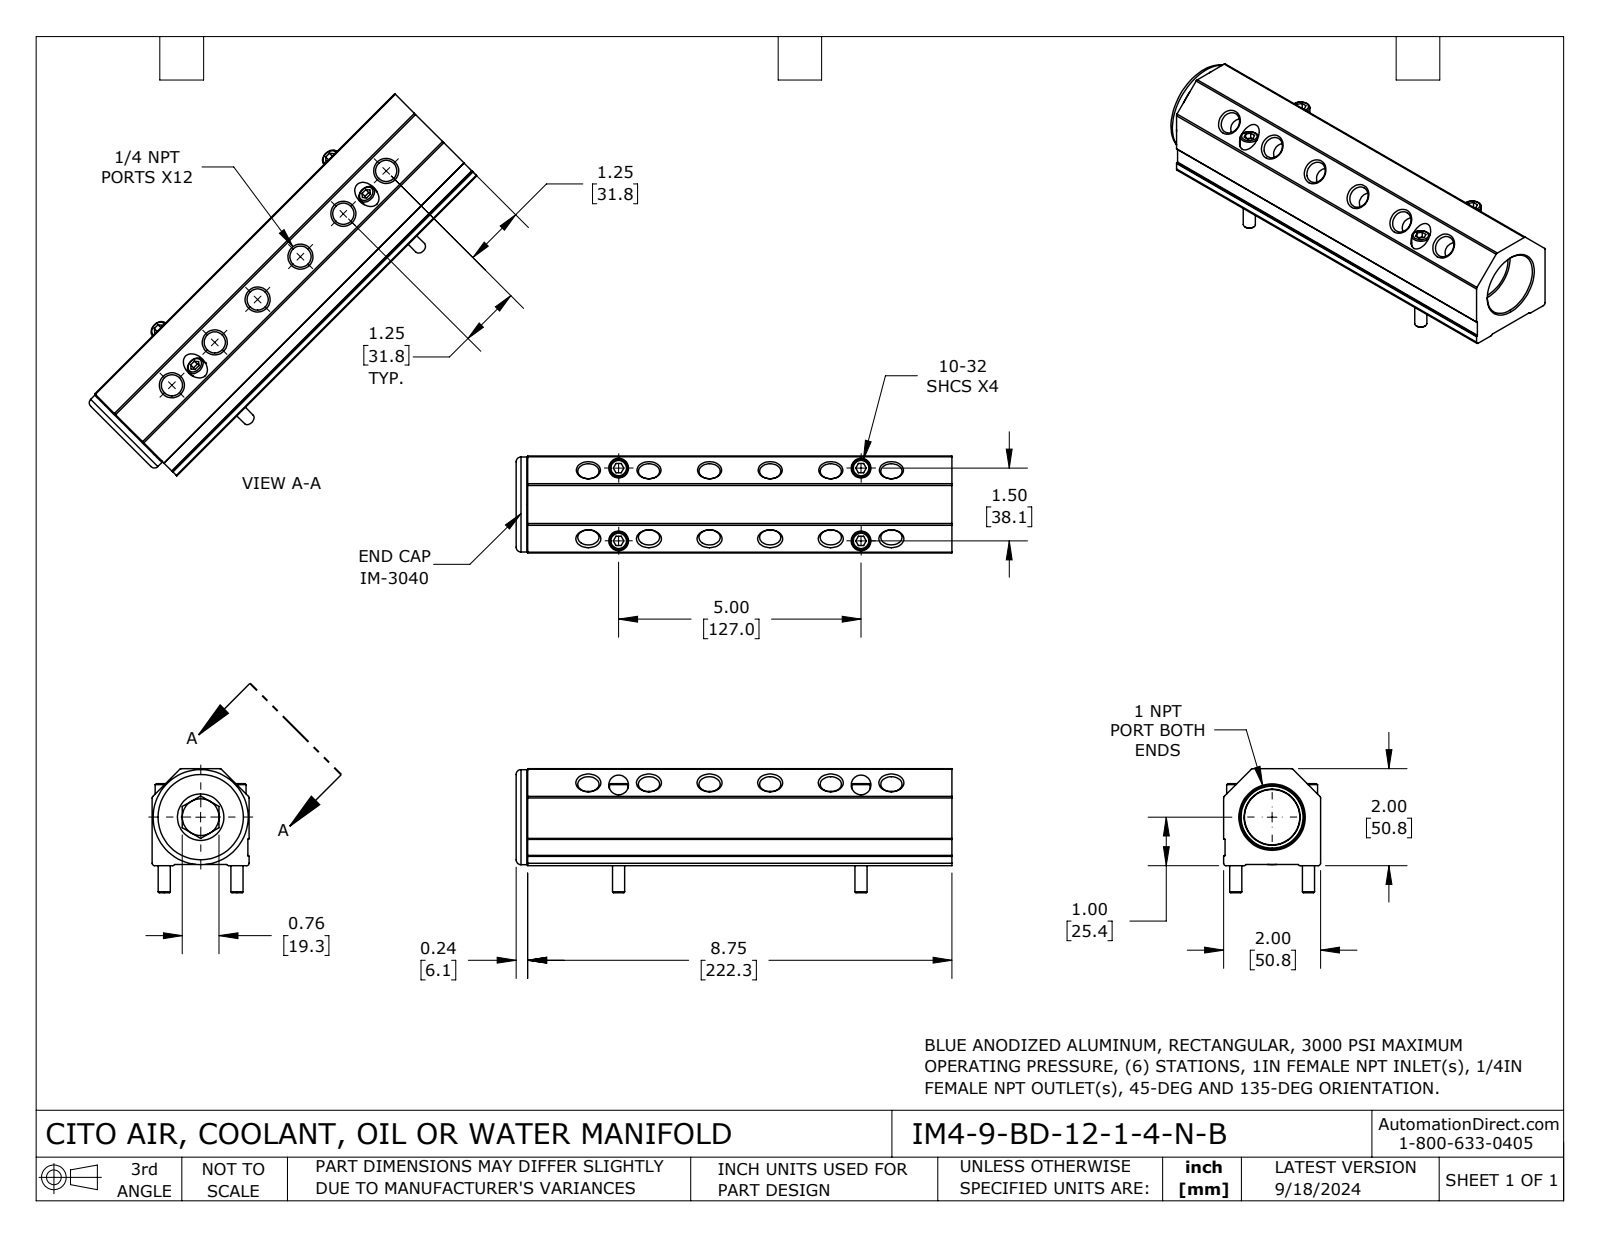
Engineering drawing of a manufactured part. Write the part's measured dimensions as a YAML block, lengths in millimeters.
part_name: "IM4-9-BD-12-1-4-N-B"
step_written_by: "SolidWorks 2023 (CONFIG_CONTROL_DESIGN)"
units: millimeters
bodies: {solids: 6, faces: 229, planar: 81, cylindrical: 82, other: 66}
overall_size: [228.3, 65, 50.8]
volume: 366600
surface_area: 84130
round_holes:
  - {diameter: 11.1, count: 12}
  - {diameter: 6.8, count: 4}
  - {diameter: 10.3, count: 4}
  - {diameter: 19.3, count: 1}
  - {diameter: 29.4, count: 1}
  - {diameter: 41.6, count: 1}
round_bosses_or_shafts:
  - {diameter: 9.5, count: 4}
  - {diameter: 6.4, count: 4}
  - {diameter: 49.8, count: 1}
  - {diameter: 34.5, count: 1}
  - {diameter: 32.8, count: 1}
  - {diameter: 29, count: 1}
partial_cylinders:
  - {radius: 1.3, count: 8}
  - {radius: 0.3, count: 4}
face_to_face_distances: [50.8, 50.2, 0.6, 0.7, 50.1, 222.3, 6.1, 228.3, 19.4, 13.3]
hole_center_spacings: [31.8, 63.5, 95.3, 127, 38.1, 132.6, 158.8]
